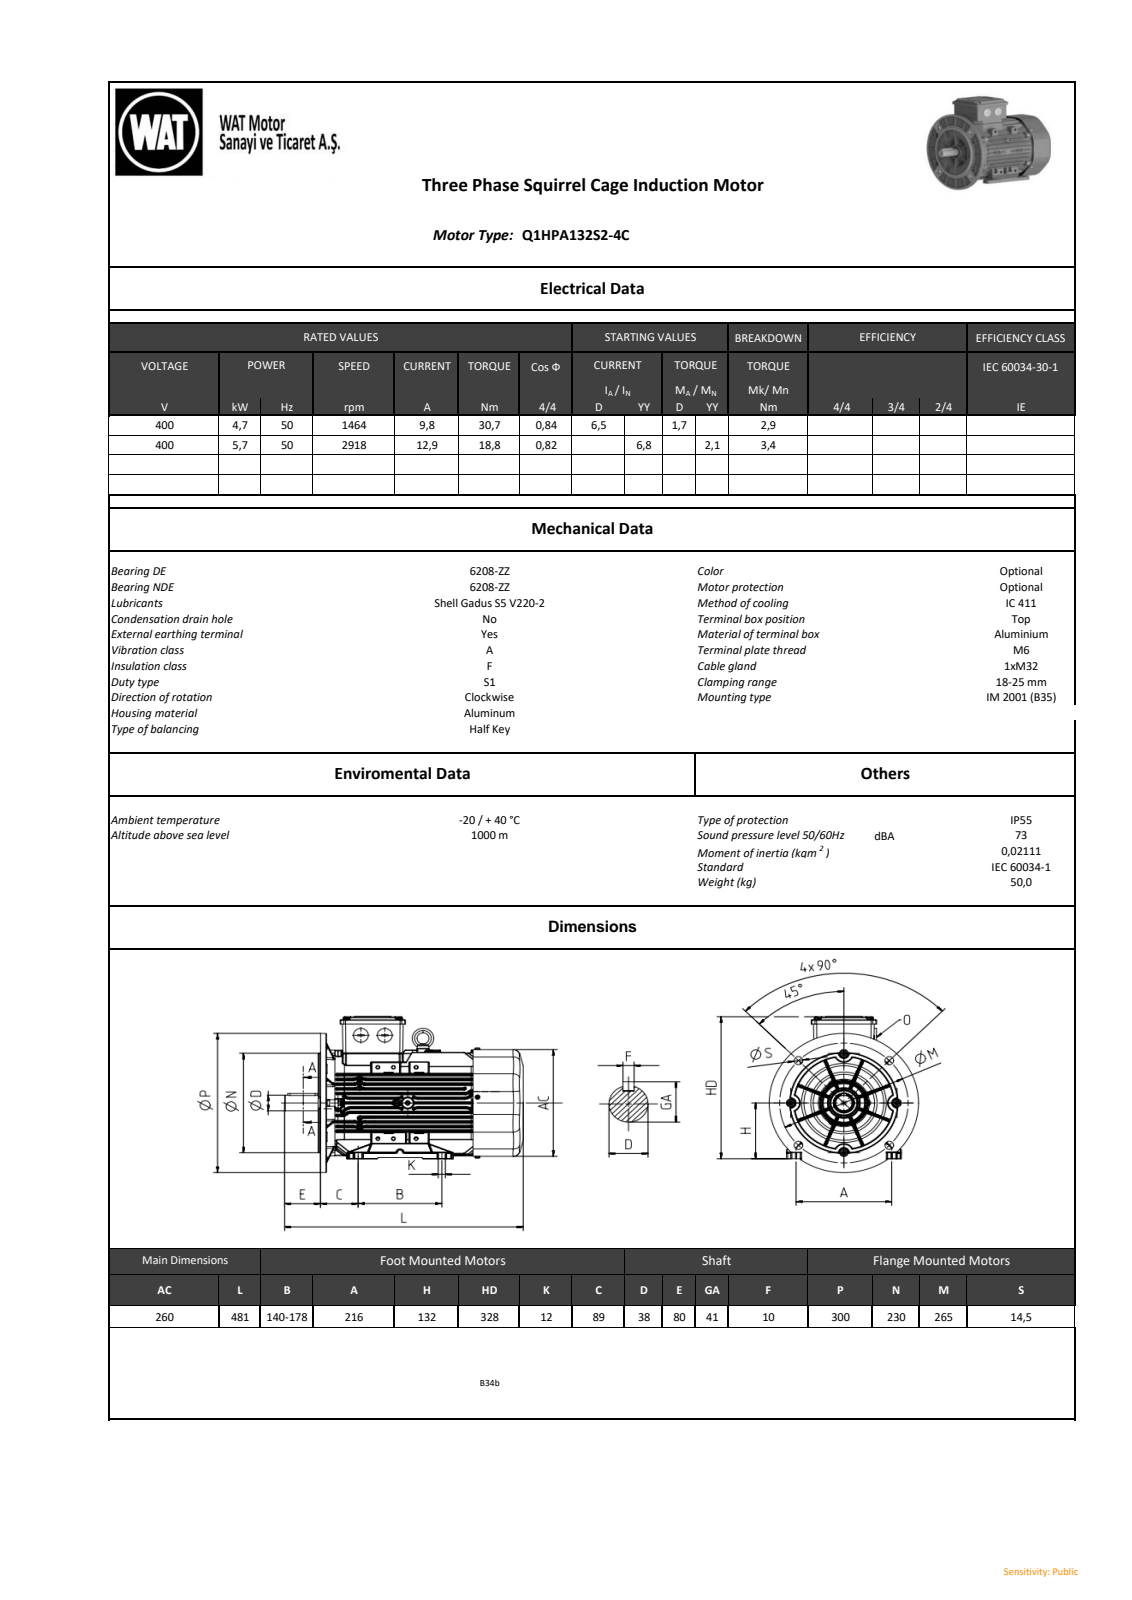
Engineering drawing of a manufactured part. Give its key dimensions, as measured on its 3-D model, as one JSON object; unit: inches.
{"part_name": "QH series_ 132_B35_stp_objects", "step_written_by": "SIEMENS PLM Software NX2206.8101 (AP203_CONFIGURATION_CONTROLLED_3D_DESIGN_OF_MECHANICAL_PARTS_AND_ASSEMBLIES_MIM_LF)", "units": "inches", "bodies": {"solids": 0, "faces": 7006, "planar": 1725, "cylindrical": 3027, "other": 2254}, "overall_size": [18.917, 13.393, 11.809], "round_holes": [[0.334, 1], [0.334, 1], [0.472, 1], [0.551, 1], [0.961, 1], [3.228, 1], [7.087, 1]], "round_bosses_or_shafts": [[0.315, 11], [0.512, 4], [1.496, 3], [9.075, 1], [9.055, 1], [3.416, 1], [1.772, 1], [1.575, 1]], "partial_cylinders_radius": [[0.031, 850], [0.039, 800], [0.02, 118], [0.118, 74], [0.079, 54], [0.197, 20], [2.362, 16], [0.394, 12]], "face_to_face_distances": [0.41, 0.416, 0.059, 0.82, 0.405, 4.944, 3.309, 4.535, 4.13, 0.374], "hole_center_spacings": [7.044]}
